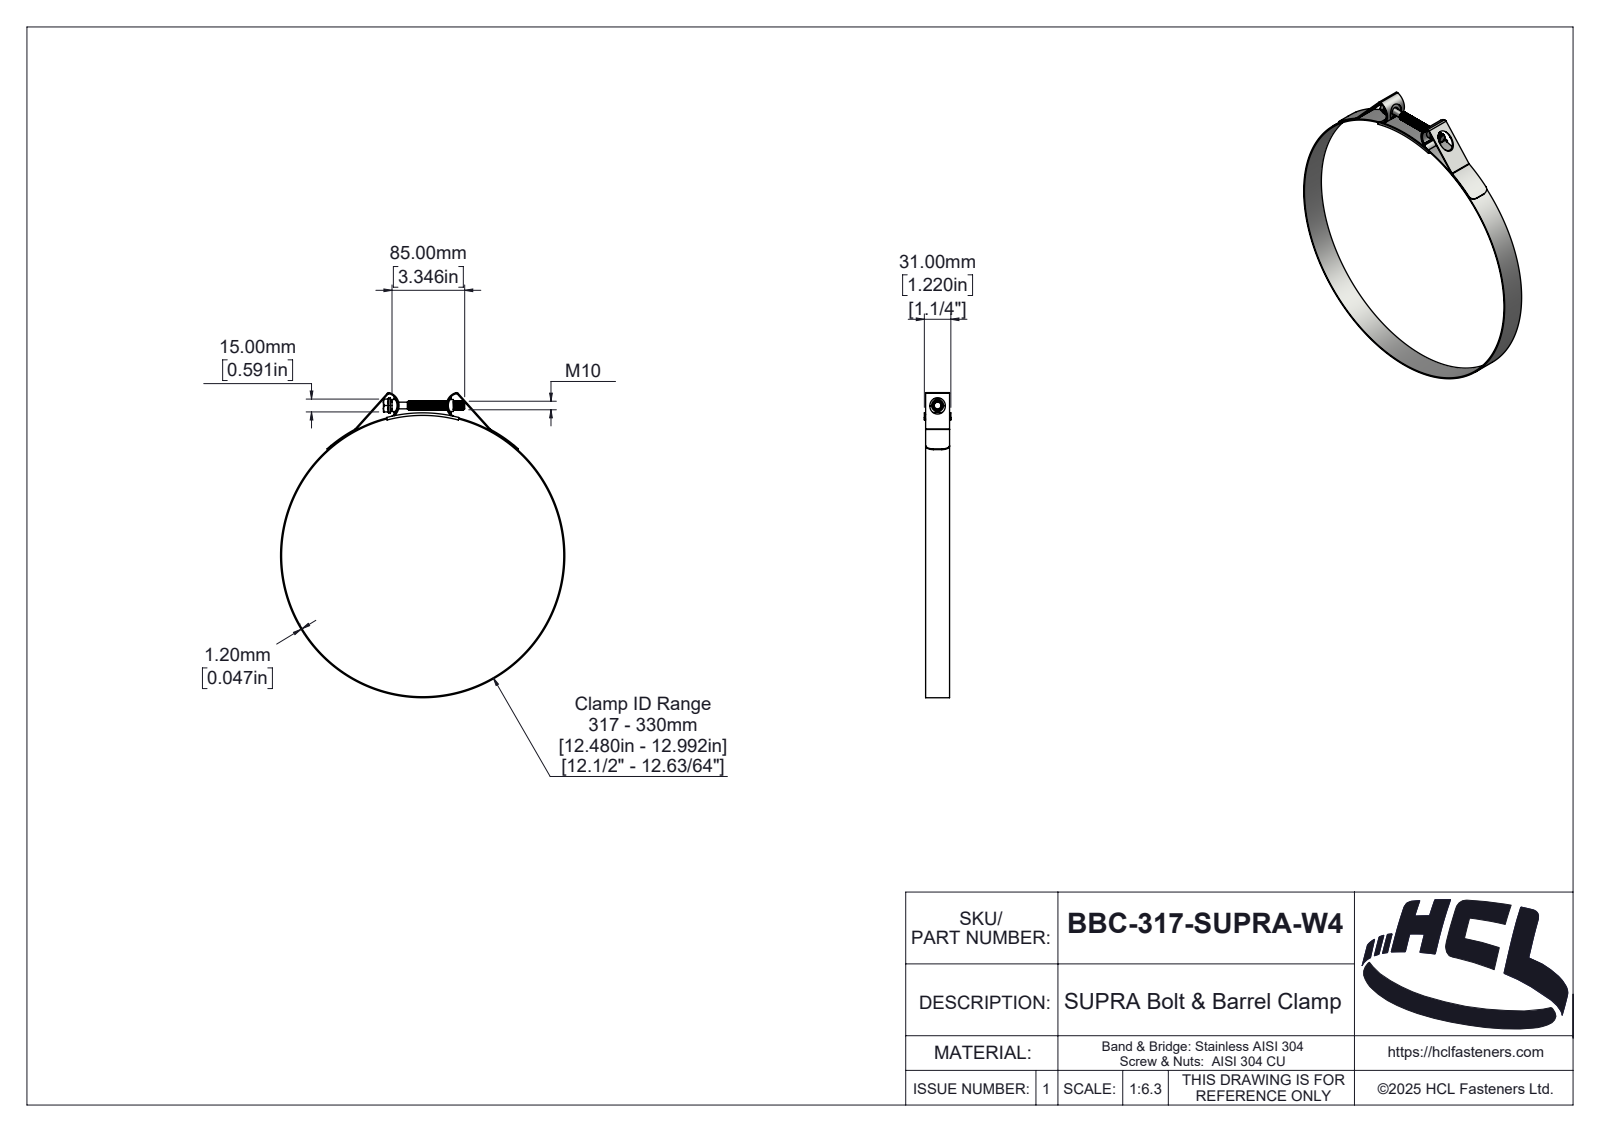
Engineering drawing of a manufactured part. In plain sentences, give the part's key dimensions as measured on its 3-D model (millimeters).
The part is named "BBC-317-SUPRA-W4". Its 3-D file was written by "SolidWorks 2025 (AUTOMOTIVE_DESIGN)". It is 5 solids with 380 faces: 50 planar, 243 cylindrical and 87 other. Overall it measures 356.62 by 332.4 by 31 millimeters. Its volume is 52 760 cubic millimeters and its surface area 83 714 square millimeters. Round holes: 1 of diameter 330. Round bosses or shafts: 1 of diameter 332.4, 1 of diameter 17.32, 1 of diameter 14, 1 of diameter 10, 1 of diameter 7.8. Partial cylindrical surfaces (rounded edges, fillets, slot ends): 4 of radius 1, 2 of radius 1.3, 2 of radius 2, 2 of radius 2.5, 2 of radius 3.2, 2 of radius 9, 2 of radius 13.31, 2 of radius 14.31. The main face-to-face distances are 1.2, 28, 1.5, 29.5, 29.8, 28.3, 31, 28.6, 15, 2.5.
